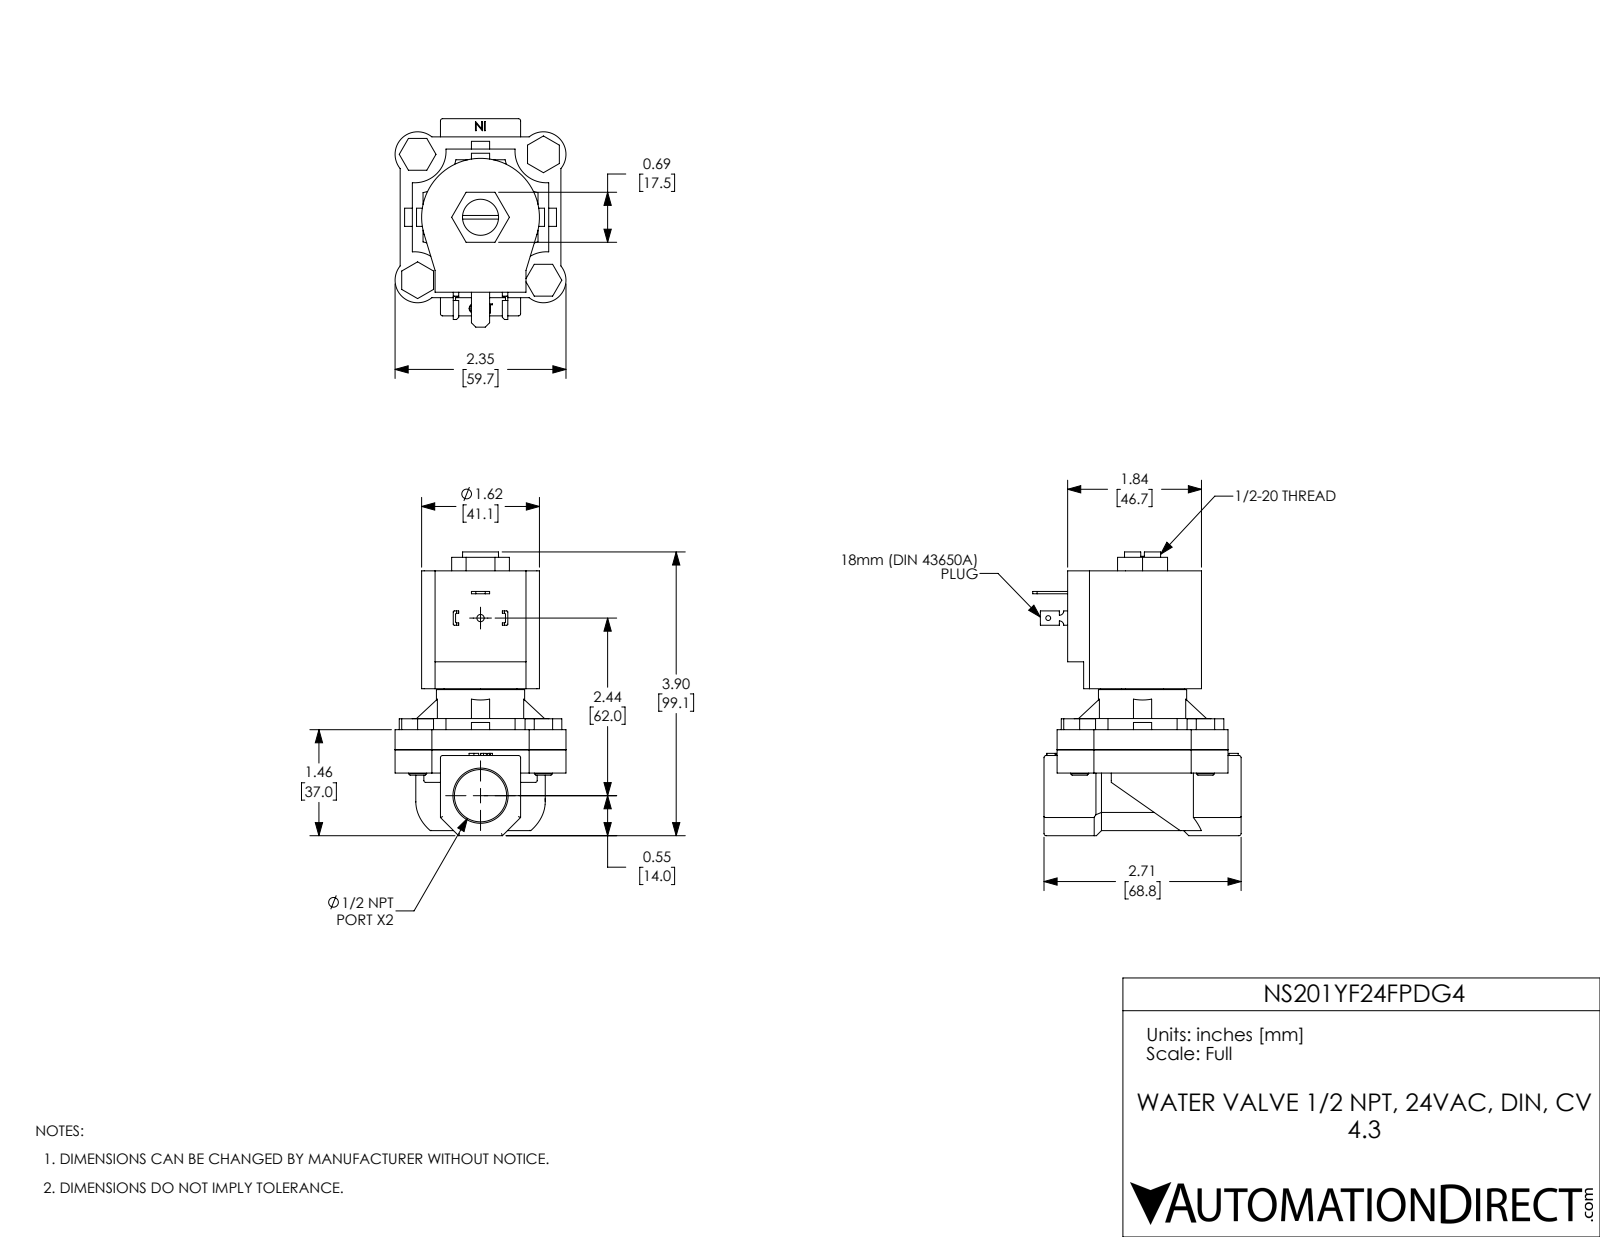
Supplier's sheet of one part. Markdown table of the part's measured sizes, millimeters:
| quantity | value |
| --- | --- |
| part name | NS201YF24FPDG4 |
| STEP written by | SolidWorks 2017 (AUTOMOTIVE_DESIGN) |
| units | millimeters |
| bodies | 11 solids, 385 faces (239 planar, 113 cylindrical, 33 other) |
| overall size | 99.1 × 72.8 × 59.7 |
| volume | 165 000 mm³ |
| surface area | 43 540 mm² |
| round holes (diameter × count) | 6.4 × 4, 1.7 × 1, 2.5 × 1, 12.6 × 1, 13 × 1, 18.3 × 1, 29.3 × 1 |
| round bosses / shafts (diameter × count) | 6.3 × 4, 30.8 × 1 |
| partial cylindrical surfaces (radius × count) | 0.8 × 15, 0.4 × 8, 7.9 × 4, 11 × 4, 14.7 × 4, 1.5 × 2, 20.6 × 1, 22.6 × 1 |
| main face-to-face distances | 7, 62.5, 55.4, 8.1, 15.1, 70.6, 14.1, 42.1, 6.4, 28 |
| hole center spacings | 31.1, 43.9, 62.1, 62 |
